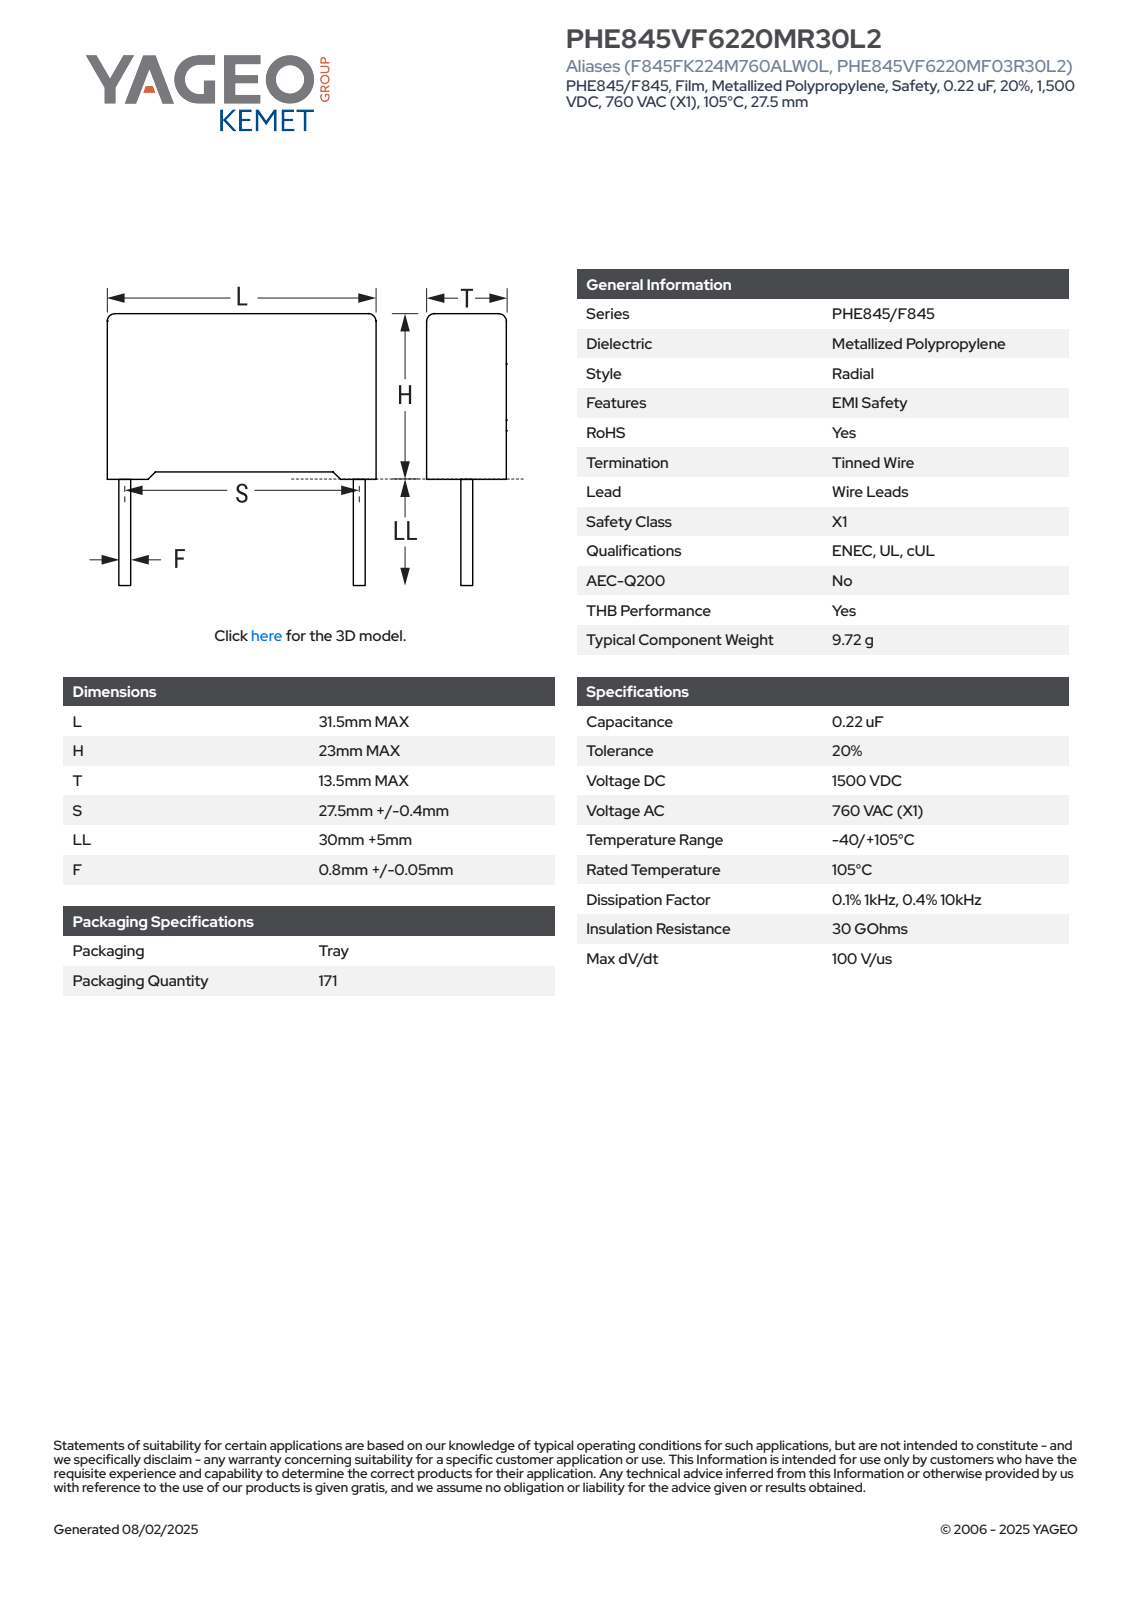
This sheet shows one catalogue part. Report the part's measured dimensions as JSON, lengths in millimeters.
{"part_name": "CFR_RB2_31.5X23X13.5_L31.5H23T13.5S27.5LL35F0.85", "step_written_by": "SolidWorks 2021 (AUTOMOTIVE_DESIGN)", "units": "millimeters", "bodies": {"solids": 4, "faces": 85, "planar": 77, "cylindrical": 8, "other": 0}, "overall_size": [58, 31.5, 13.51], "volume_mm3": 9515, "surface_area_mm2": 3156, "round_bosses_or_shafts": [[0.85, 2]], "partial_cylinders_radius": [[0.5, 4]], "face_to_face_distances": [13.5, 22.21, 31.5, 22.25, 0.75, 0.79, 23, 1.05, 30.45, 12.45]}
